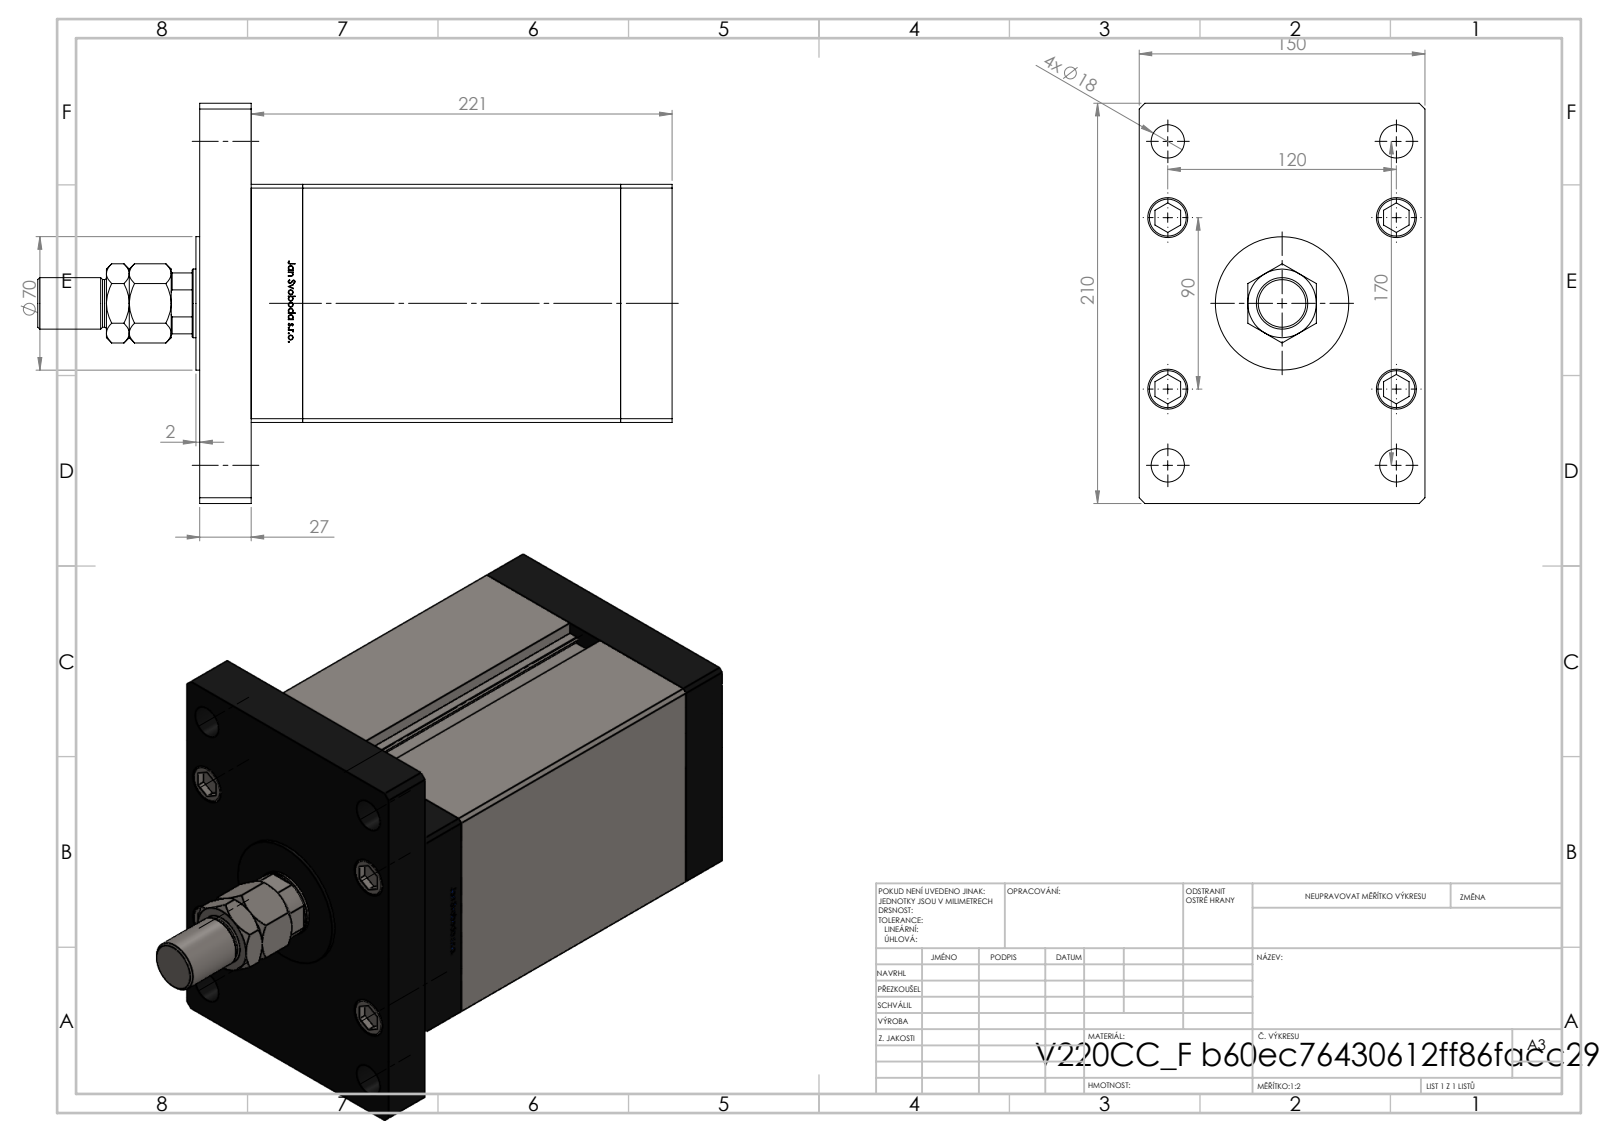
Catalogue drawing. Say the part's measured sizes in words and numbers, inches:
The part is named "V220C BACK_F; V220C_F; ALLEN BOLT; MTA (+3 more)". Its 3-D file was written by "SolidWorks 2019 (CONFIG_CONTROL_DESIGN)". It is 20 solids with 1359 faces: 532 planar, 191 cylindrical and 636 other. Overall it measures 13.11 by 8.268 by 5.906 inches. Its volume is 269.8 cubic inches and its surface area 746.4 square inches. Round holes: 9 of diameter 0.689, 5 of diameter 0.866, 4 of diameter 0.63, 4 of diameter 0.827, 2 of diameter 0.079, 2 of diameter 0.518, 1 of diameter 1.004, 1 of diameter 1.417, 1 of diameter 1.476. Round bosses or shafts: 9 of diameter 0.315, 5 of diameter 0.827, 1 of diameter 3.15, 1 of diameter 2.756, 1 of diameter 1.063, 1 of diameter 0.984. Partial cylindrical surfaces (rounded edges, fillets, slot ends): 2 of radius 0.037, 1 of radius 0.689. The main face-to-face distances are 1.063, 7.638, 8.701, 5.906, 4.921, 6.575, 2.126, 9.764, 1.319, 0.256. The hole center spacings are 2.008, 1.575, 2.953, 4.096, 4.724, 4.98, 5.118, 6.965.
